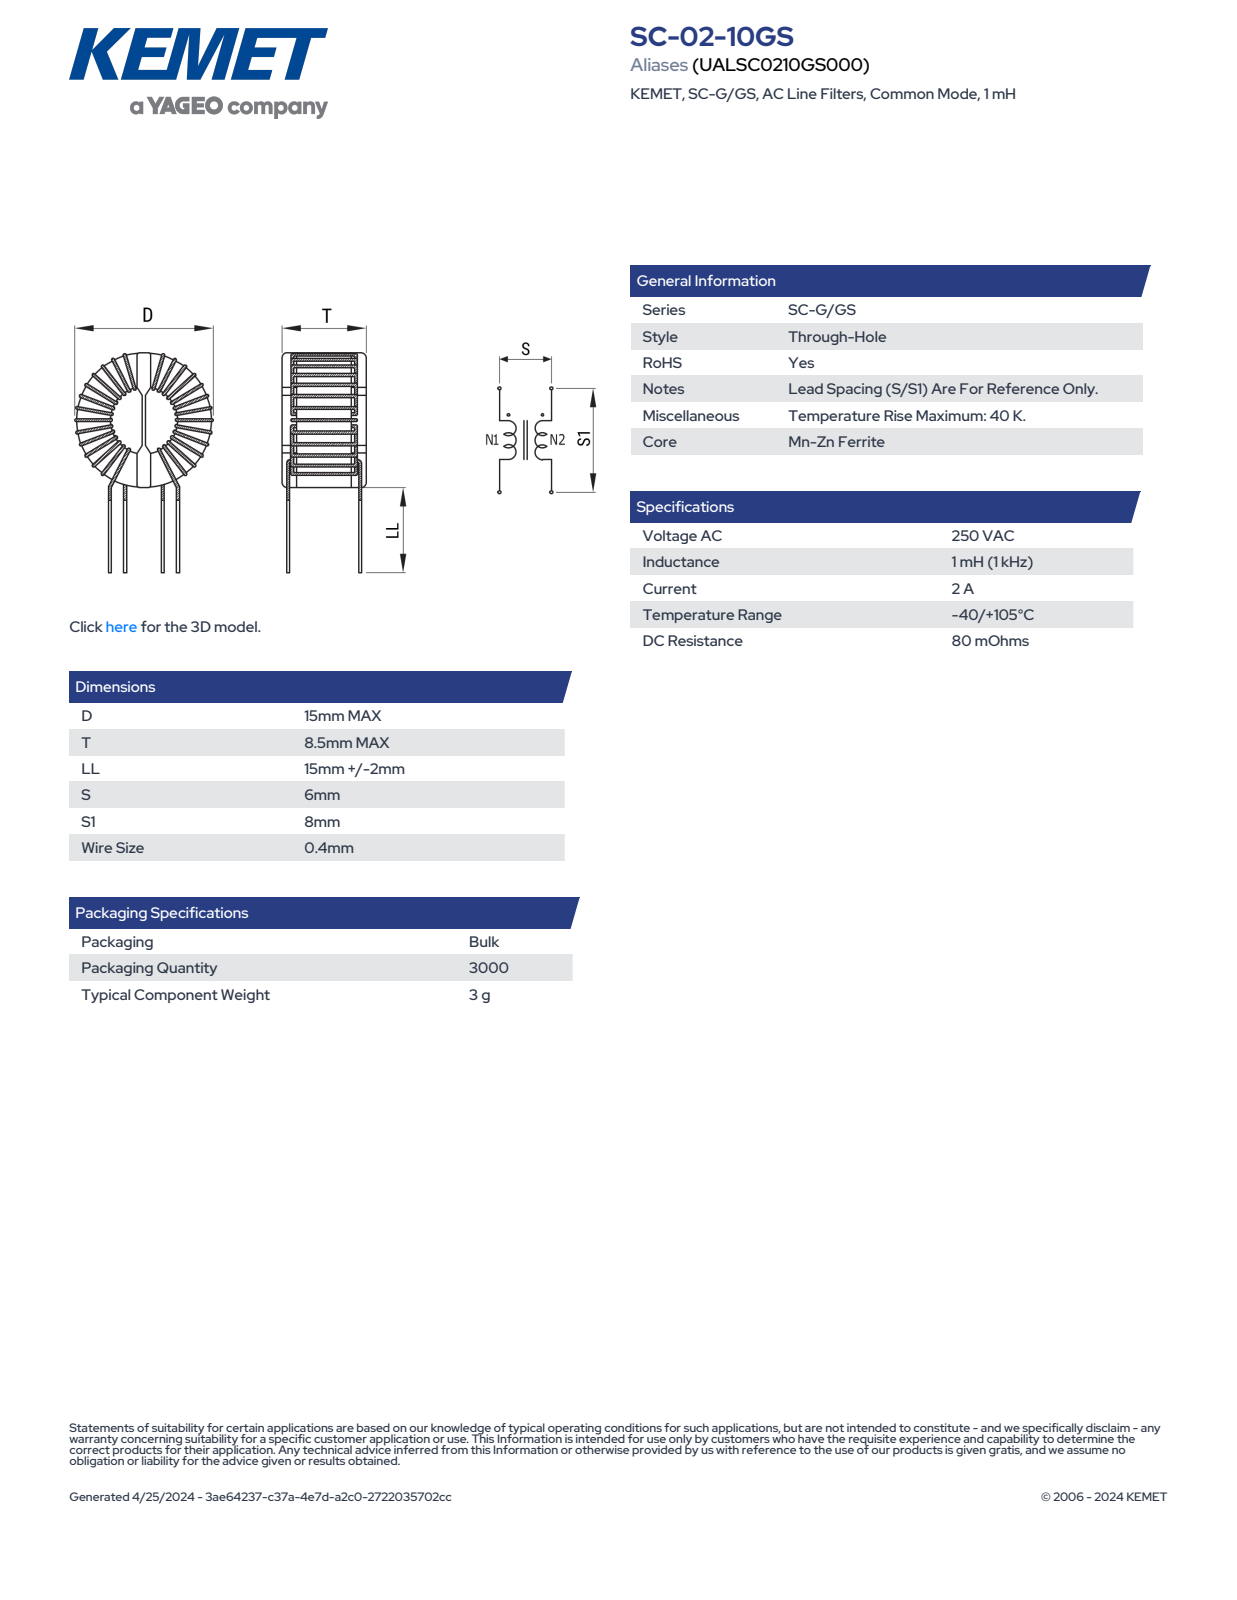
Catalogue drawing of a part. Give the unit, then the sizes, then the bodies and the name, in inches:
Units: inches
Overall size (bounding box): 1.117 × 0.591 × 0.335
Round bosses / shafts (diameter × count): ⌀0.016 ×8
Partial cylindrical surfaces — rounded edges, fillets, slot ends (radius × count): R0.008 ×16, R0.084 ×1, R0.105 ×1, R0.115 ×1, R0.118 ×1, R0.217 ×1, R0.22 ×1, R0.24 ×1
Main face-to-face distances: 0.033, 0.301, 0.047, 0.079, 0.268, 0.126, 0.031, 0.335, 0.045, 0.081
Volume: 0.062 in³ · Surface area: 1.635 in²
Bodies: 1 solid, 279 faces (121 planar, 75 cylindrical, 83 other)
Part name (STEP PRODUCT): SC-02-10GS
STEP written by: SolidWorks 2018 (AUTOMOTIVE_DESIGN)
